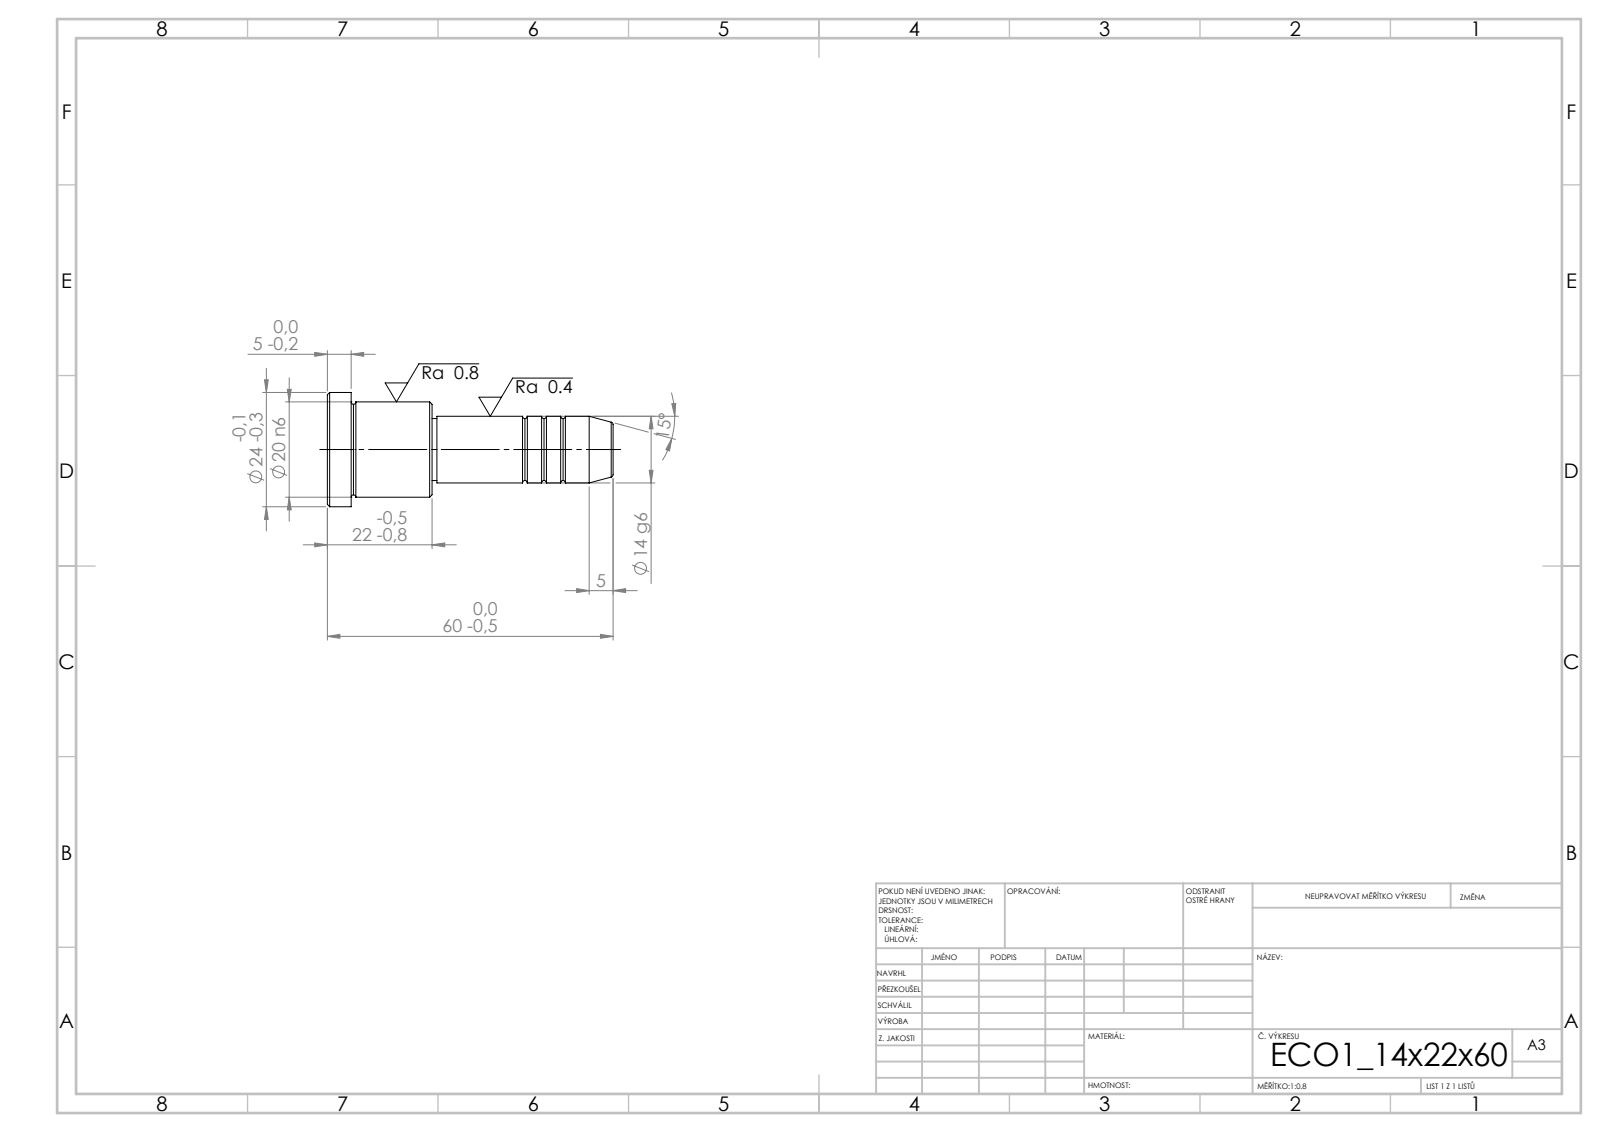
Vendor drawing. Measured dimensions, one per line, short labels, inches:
written by: SolidWorks 2019 (CONFIG_CONTROL_DESIGN)
unit: in
bodies: 1 solid, 43 faces (5 planar, 14 cylindrical, 24 other)
size: 2.362 × 0.945 × 0.945
volume: 0.806 in³; area: 6.273 in²
bosses: 1× ⌀0.945, 1× ⌀0.787, 1× ⌀0.551, 1× ⌀0.512
face distances: 0.866, 0.669, 0.197, 1.496, 2.165, 2.362, 1.457, 0.039, 0.709, 0.906
